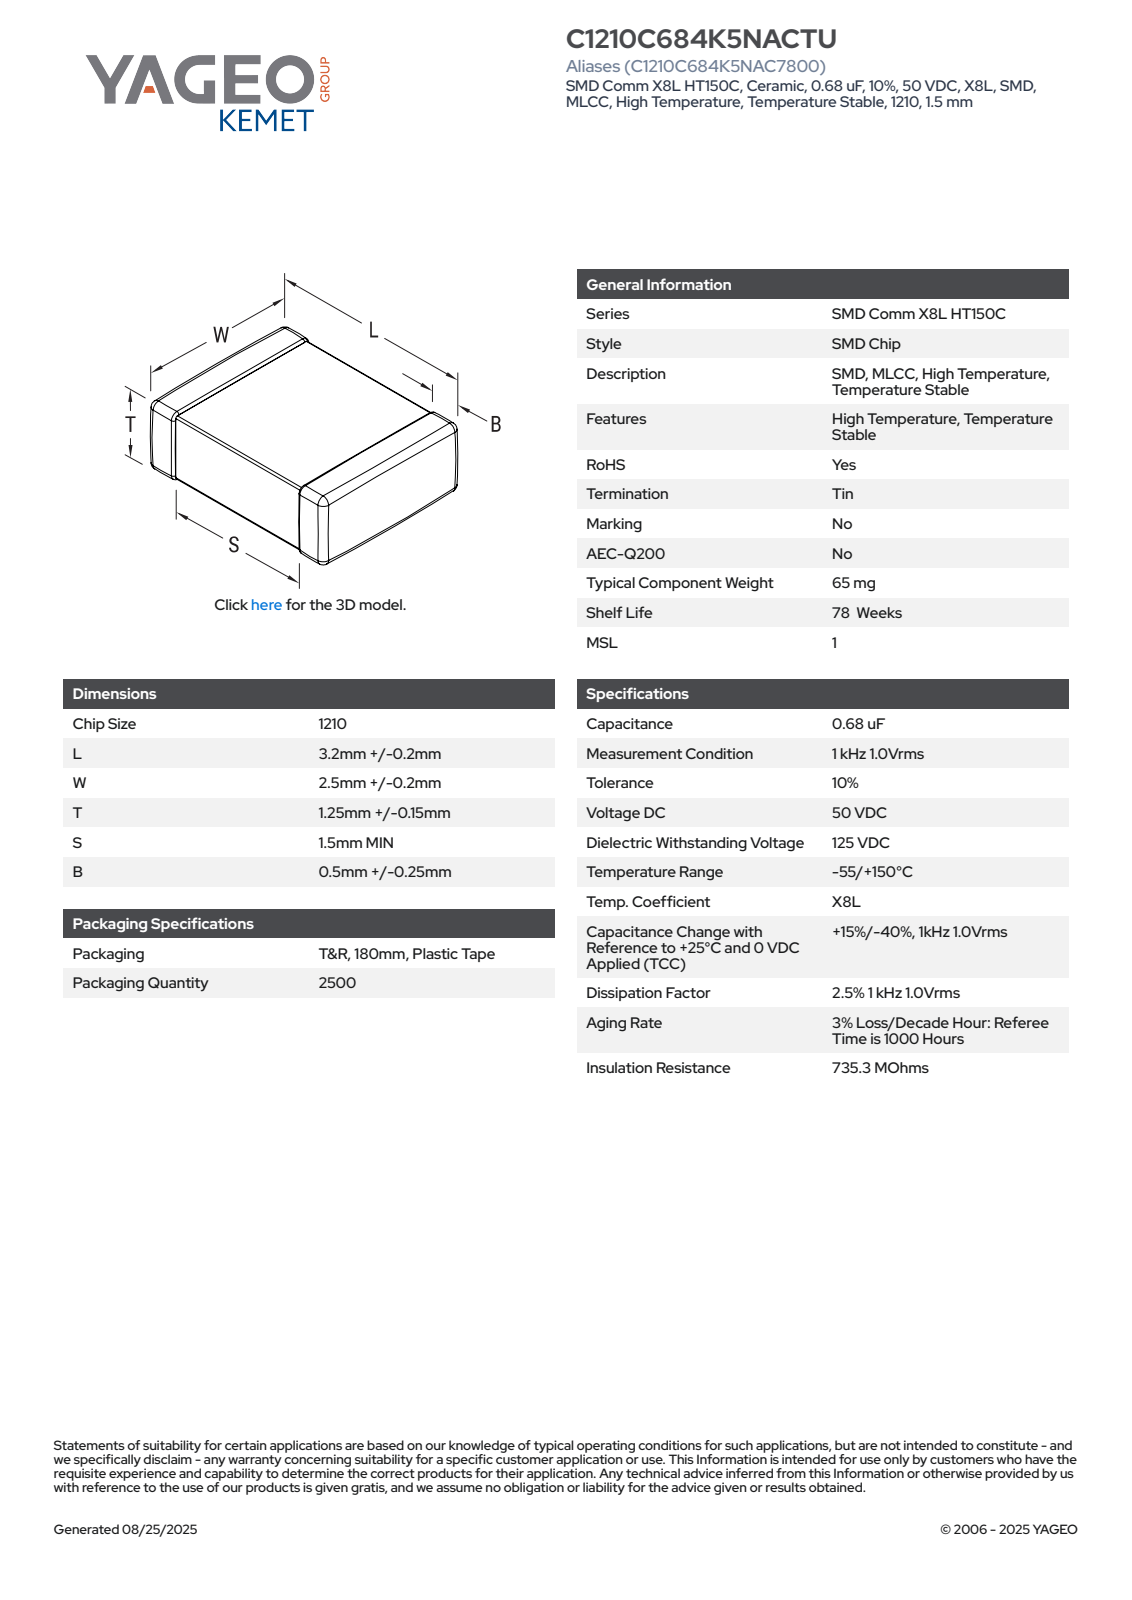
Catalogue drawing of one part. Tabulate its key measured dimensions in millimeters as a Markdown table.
| quantity | value |
| --- | --- |
| part name | CCS_CCSTD_1210_L3.4W2.7S2.5T1.4B0.5 |
| STEP written by | SolidWorks 2021 (AUTOMOTIVE_DESIGN) |
| units | millimeters |
| bodies | 4 solids, 125 faces (71 planar, 38 cylindrical, 16 other) |
| overall size | 3.4 × 2.7 × 1.4 |
| volume | 12 mm³ |
| surface area | 35 mm² |
| main face-to-face distances | 1.34, 1.28, 3.4, 1.4, 2.64, 2.58, 2.7, 1.35, 1.29, 0.4 |
